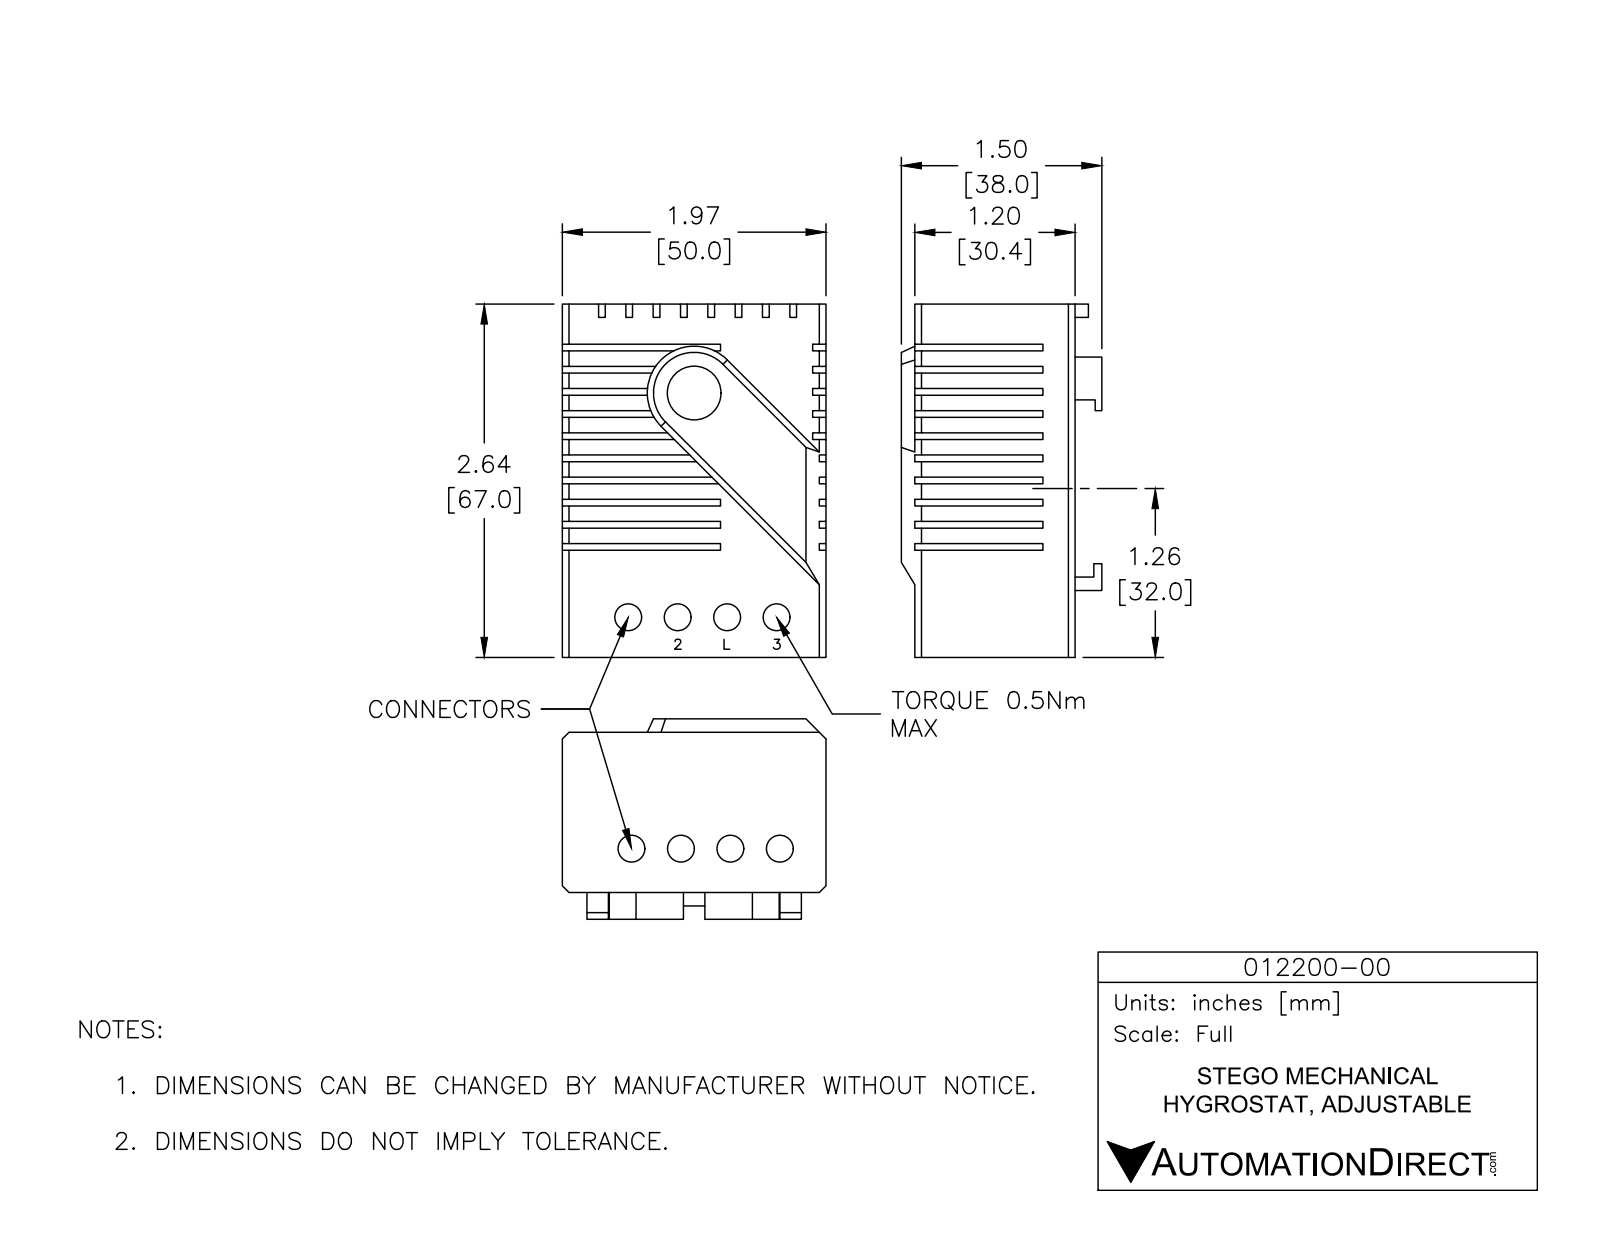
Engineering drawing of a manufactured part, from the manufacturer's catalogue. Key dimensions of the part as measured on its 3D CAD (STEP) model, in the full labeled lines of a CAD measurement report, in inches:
Part name (STEP PRODUCT): PRODUCT_NAME_2
STEP written by: ACIS (AUTOMOTIVE_DESIGN_CC2)
Units: inches
Bodies: 1 solid, 223 faces (204 planar, 18 cylindrical, 1 other)
Overall size (bounding box): 2.638 × 1.969 × 1.496
Volume: 6.125 in³ · Surface area: 31.16 in²
Round holes (diameter × count): ⌀0.2 ×8, ⌀0.4 ×1
Main face-to-face distances: 0.165, 1.196, 0.05, 0.331, 0.826, 1.969, 0.115, 0.496, 2.638, 0.215
Hole centre spacings: 0.369, 0.369, 0.738, 0.738, 0.739, 1.107, 1.107, 1.677
